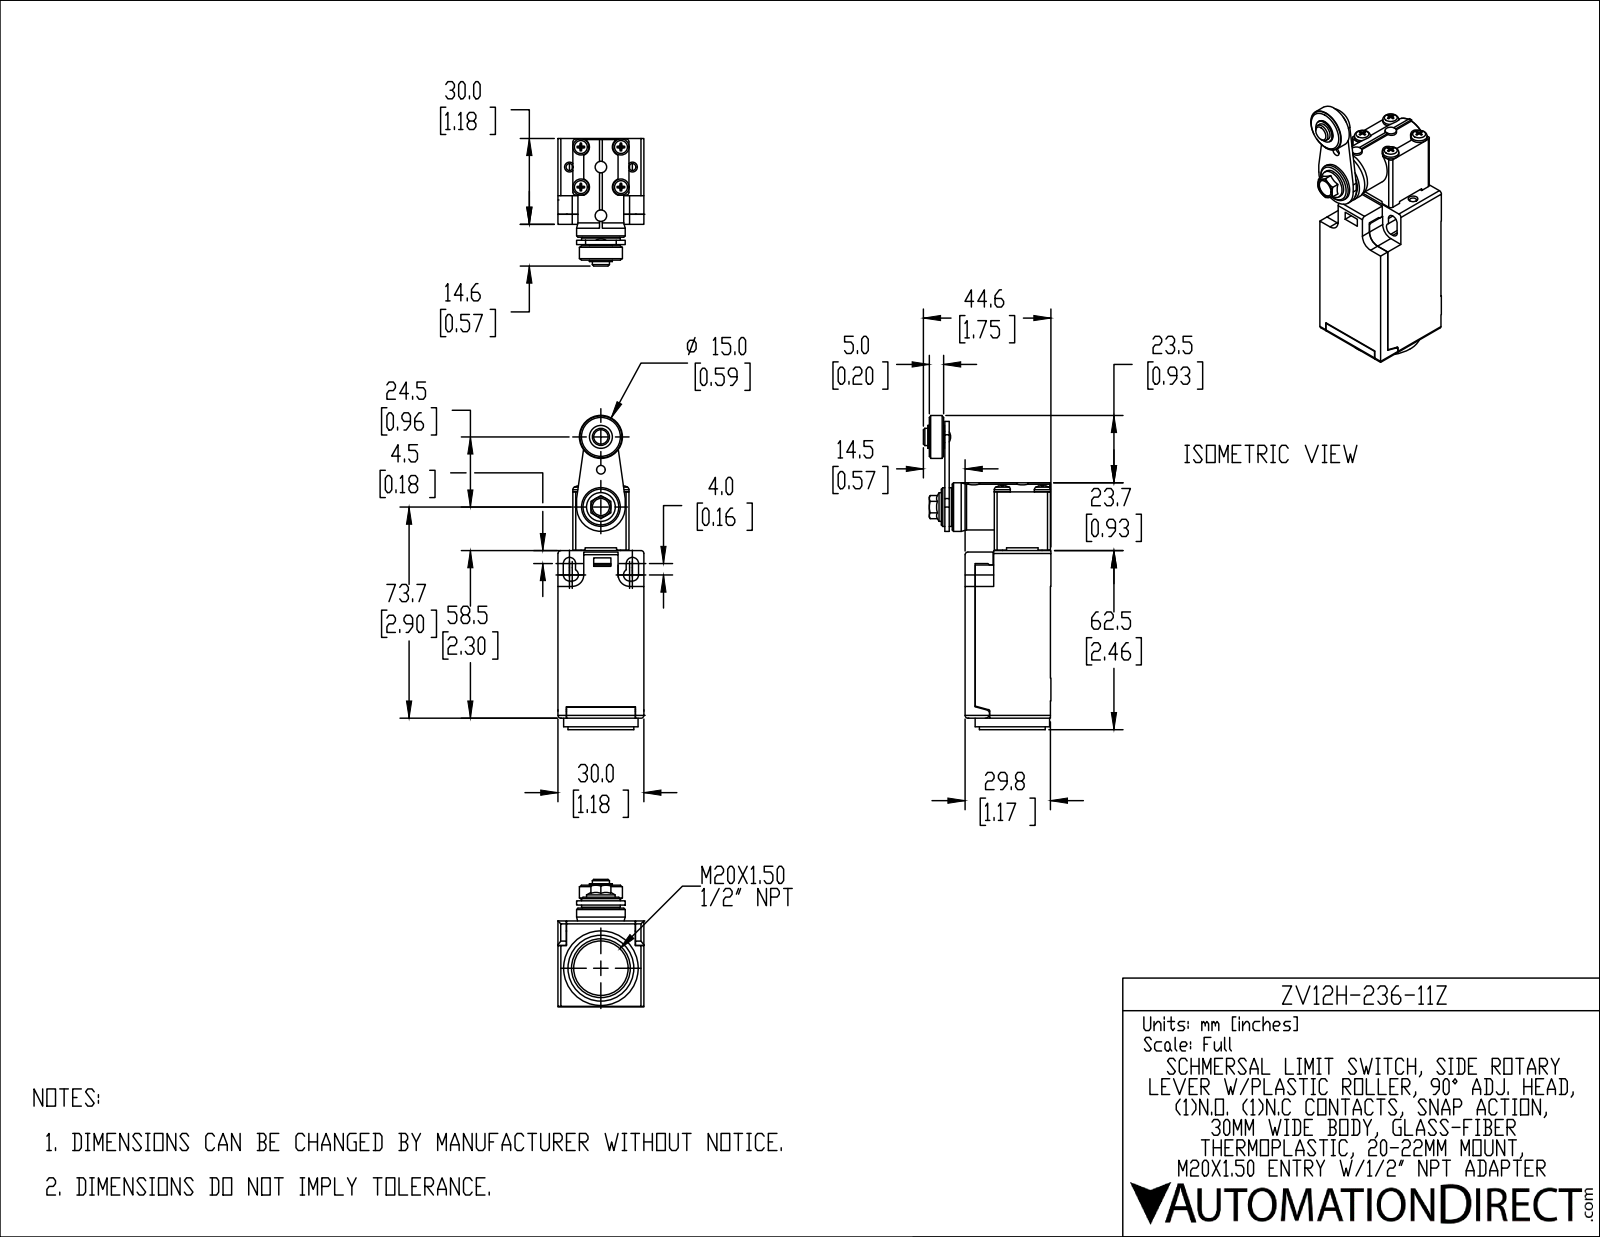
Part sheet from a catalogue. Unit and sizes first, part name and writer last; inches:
Units: inches
Overall size (bounding box): 4.319 × 1.754 × 1.181
Round holes (diameter × count): ⌀0.094 ×6, ⌀0.126 ×4, ⌀0.118 ×1, ⌀0.236 ×1, ⌀0.512 ×1, ⌀0.545 ×1, ⌀0.748 ×1
Round bosses / shafts (diameter × count): ⌀0.221 ×4, ⌀0.213 ×4, ⌀0.157 ×3, ⌀1.024 ×1, ⌀0.906 ×1, ⌀0.669 ×1, ⌀0.63 ×1, ⌀0.591 ×1
Partial cylindrical surfaces — rounded edges, fillets, slot ends (radius × count): R0.039 ×10, R0.085 ×6, R0.059 ×5, R0.118 ×4, R0.157 ×2, R0.008 ×1, R0.024 ×1, R0.213 ×1
Main face-to-face distances: 1.181, 1.035, 0.138, 1.173, 0.205, 0.976, 1.043, 0.772, 0.236, 0.157
Hole centre spacings: 0.317, 0.39, 0.551, 0.76, 0.308, 0.433, 0.454, 0.497
Volume: 3.714 in³ · Surface area: 30.13 in²
Bodies: 2 solids, 348 faces (237 planar, 84 cylindrical, 27 other)
Part name (STEP PRODUCT): ZV12H-236-11Z
STEP written by: SolidWorks 2019 (AUTOMOTIVE_DESIGN)
